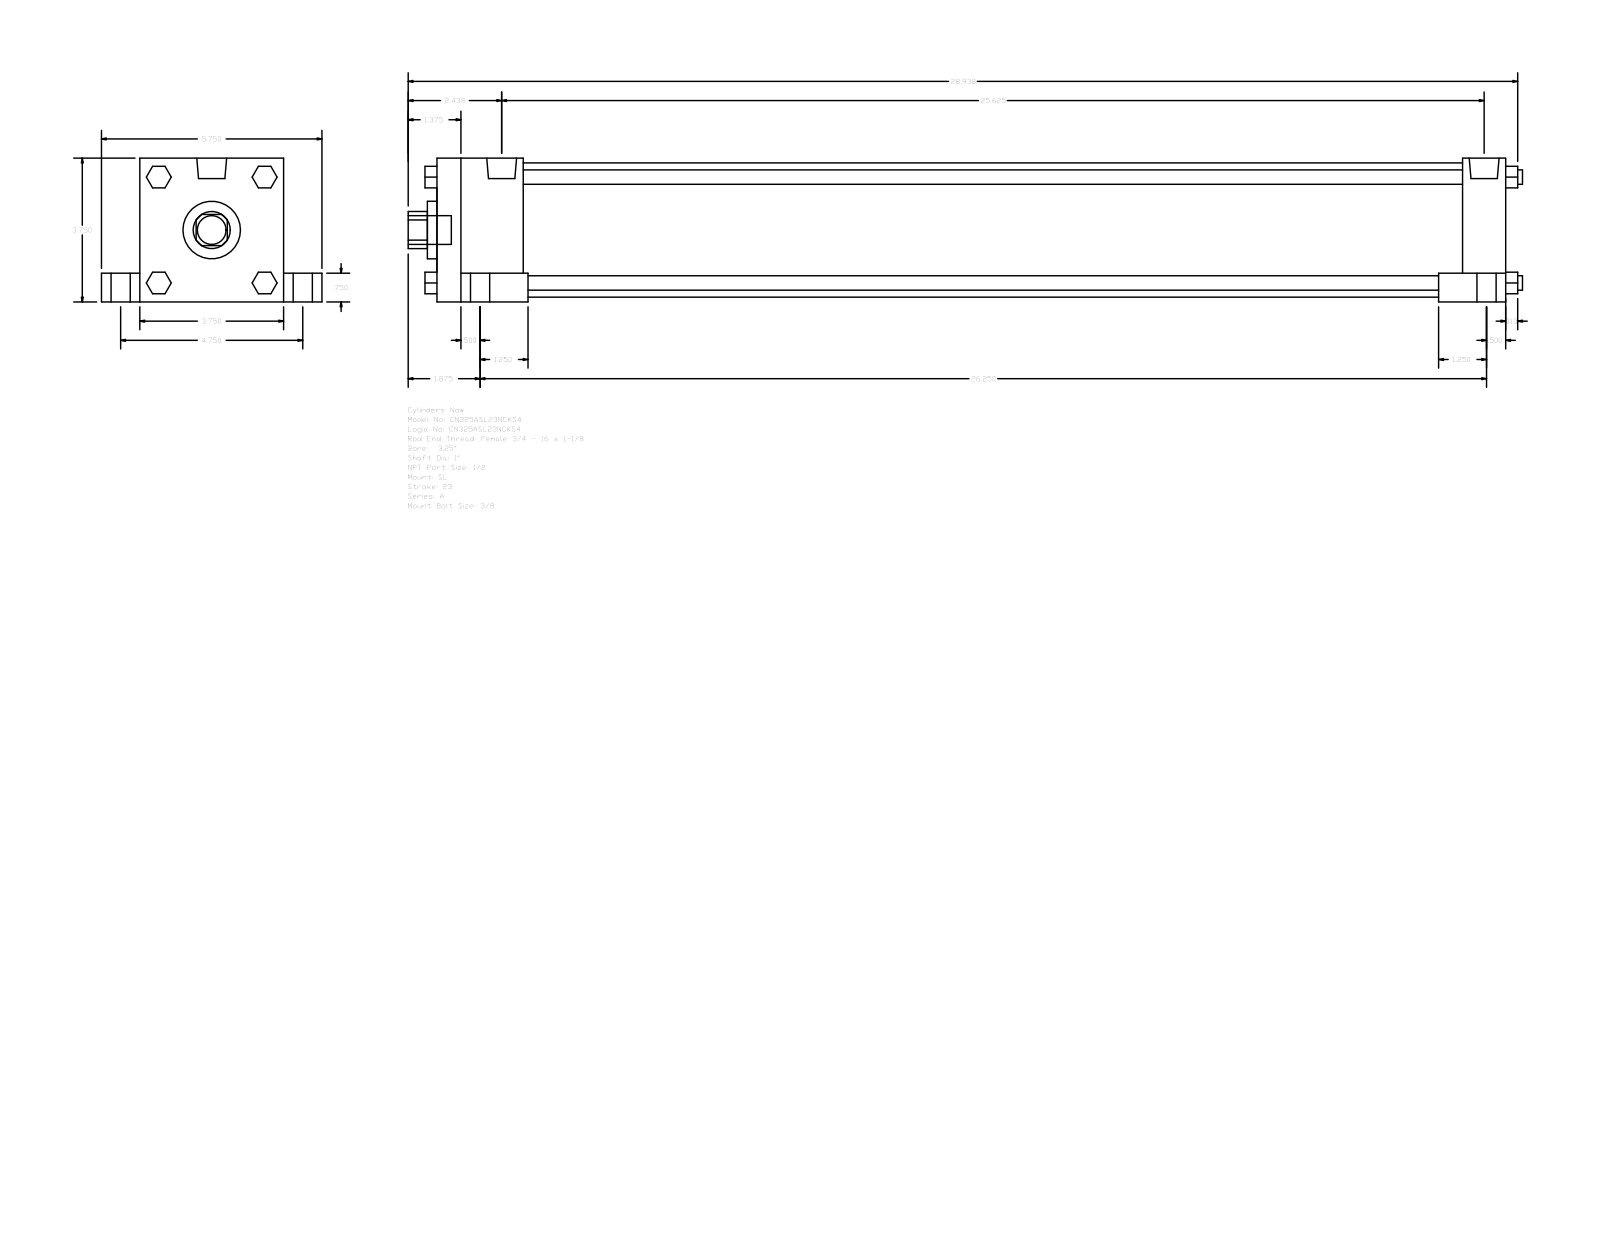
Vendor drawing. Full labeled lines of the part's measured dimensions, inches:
Part name (STEP PRODUCT): A_SL__0325_1
STEP written by: GSSL Pune (CONFIG_CONTROL_DESIGN)
Units: inches
Bodies: 0 solids, 150 faces (114 planar, 36 cylindrical, 0 other)
Overall size (bounding box): 29.063 × 5.75 × 3.75
Round holes (diameter × count): ⌀1 ×1, ⌀1.5 ×1, ⌀3.5 ×1
Round bosses / shafts (diameter × count): ⌀0.75 ×5, ⌀0.5 ×4, ⌀0.375 ×4, ⌀0.344 ×4, ⌀0.778 ×2
Partial cylindrical surfaces — rounded edges, fillets, slot ends (radius × count): R0.484 ×1
Main face-to-face distances: 3.75, 27.875, 0.75, 1, 4.75, 3, 2.25, 26.75, 24.5, 25.625
